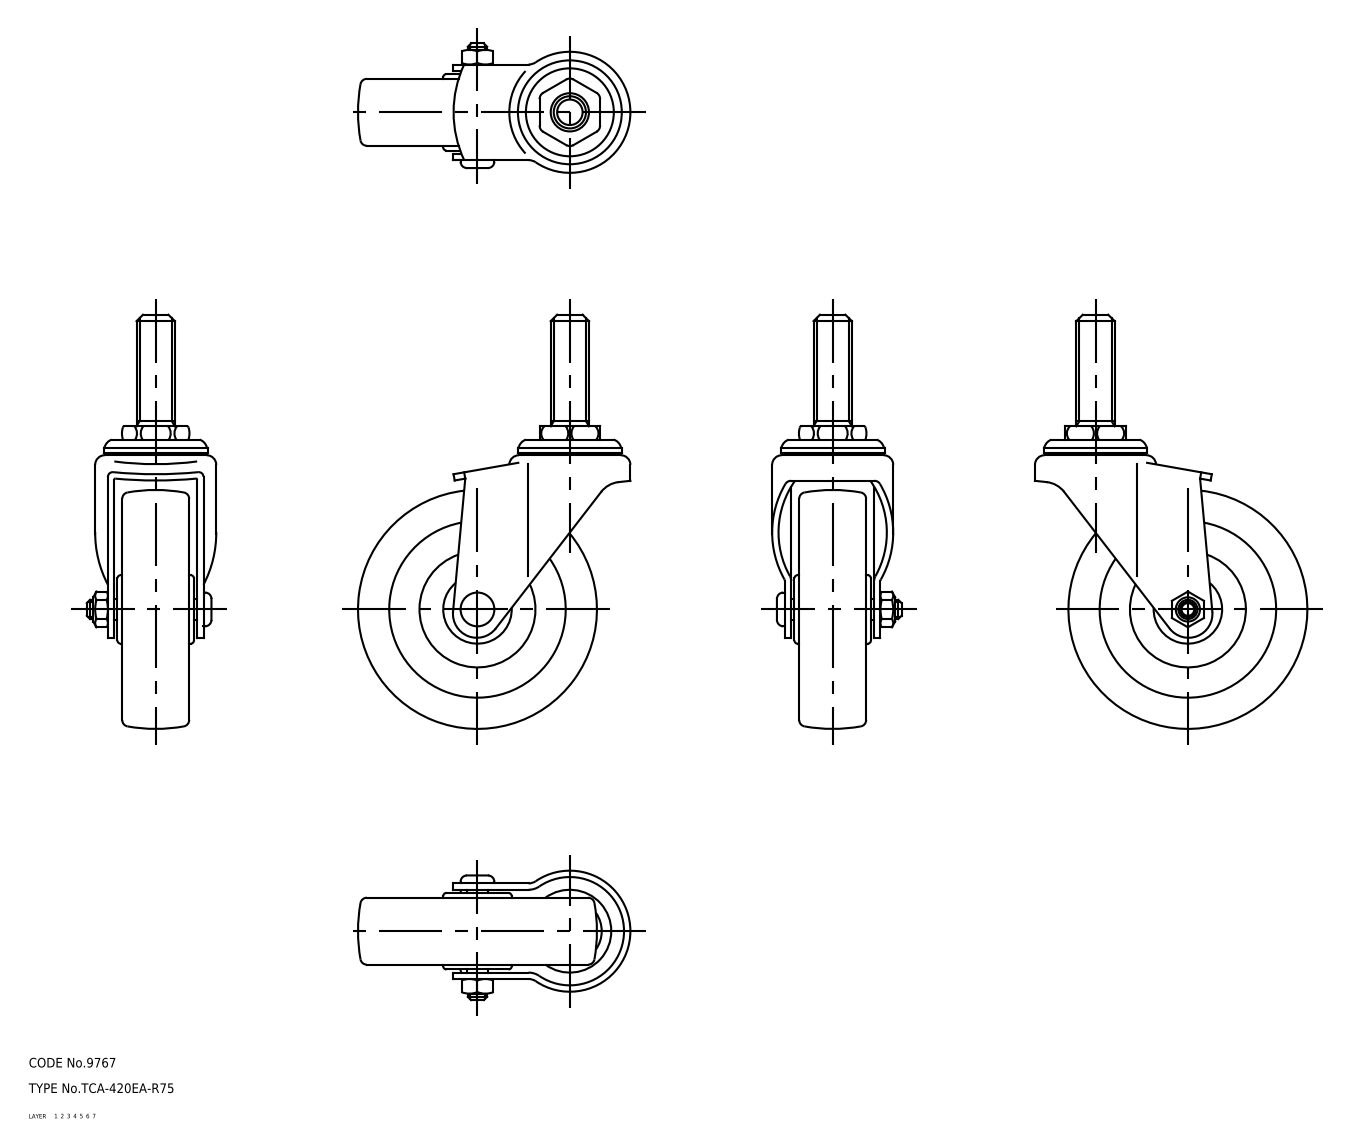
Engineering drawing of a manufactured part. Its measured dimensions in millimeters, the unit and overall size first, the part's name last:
Units: millimetres
Overall size (bounding box): 130 × 85.5 × 40.6
Volume: 111 315 mm³ · Surface area: 31 768 mm²
Bodies: 5 solids, 222 faces (0 planar, 0 cylindrical, 222 other)
Part name (STEP PRODUCT): wheel; mounting plate; main shaft; axle (+1 more)
STEP written by: CADfix (AUTOMOTIVE_DESIGN)
